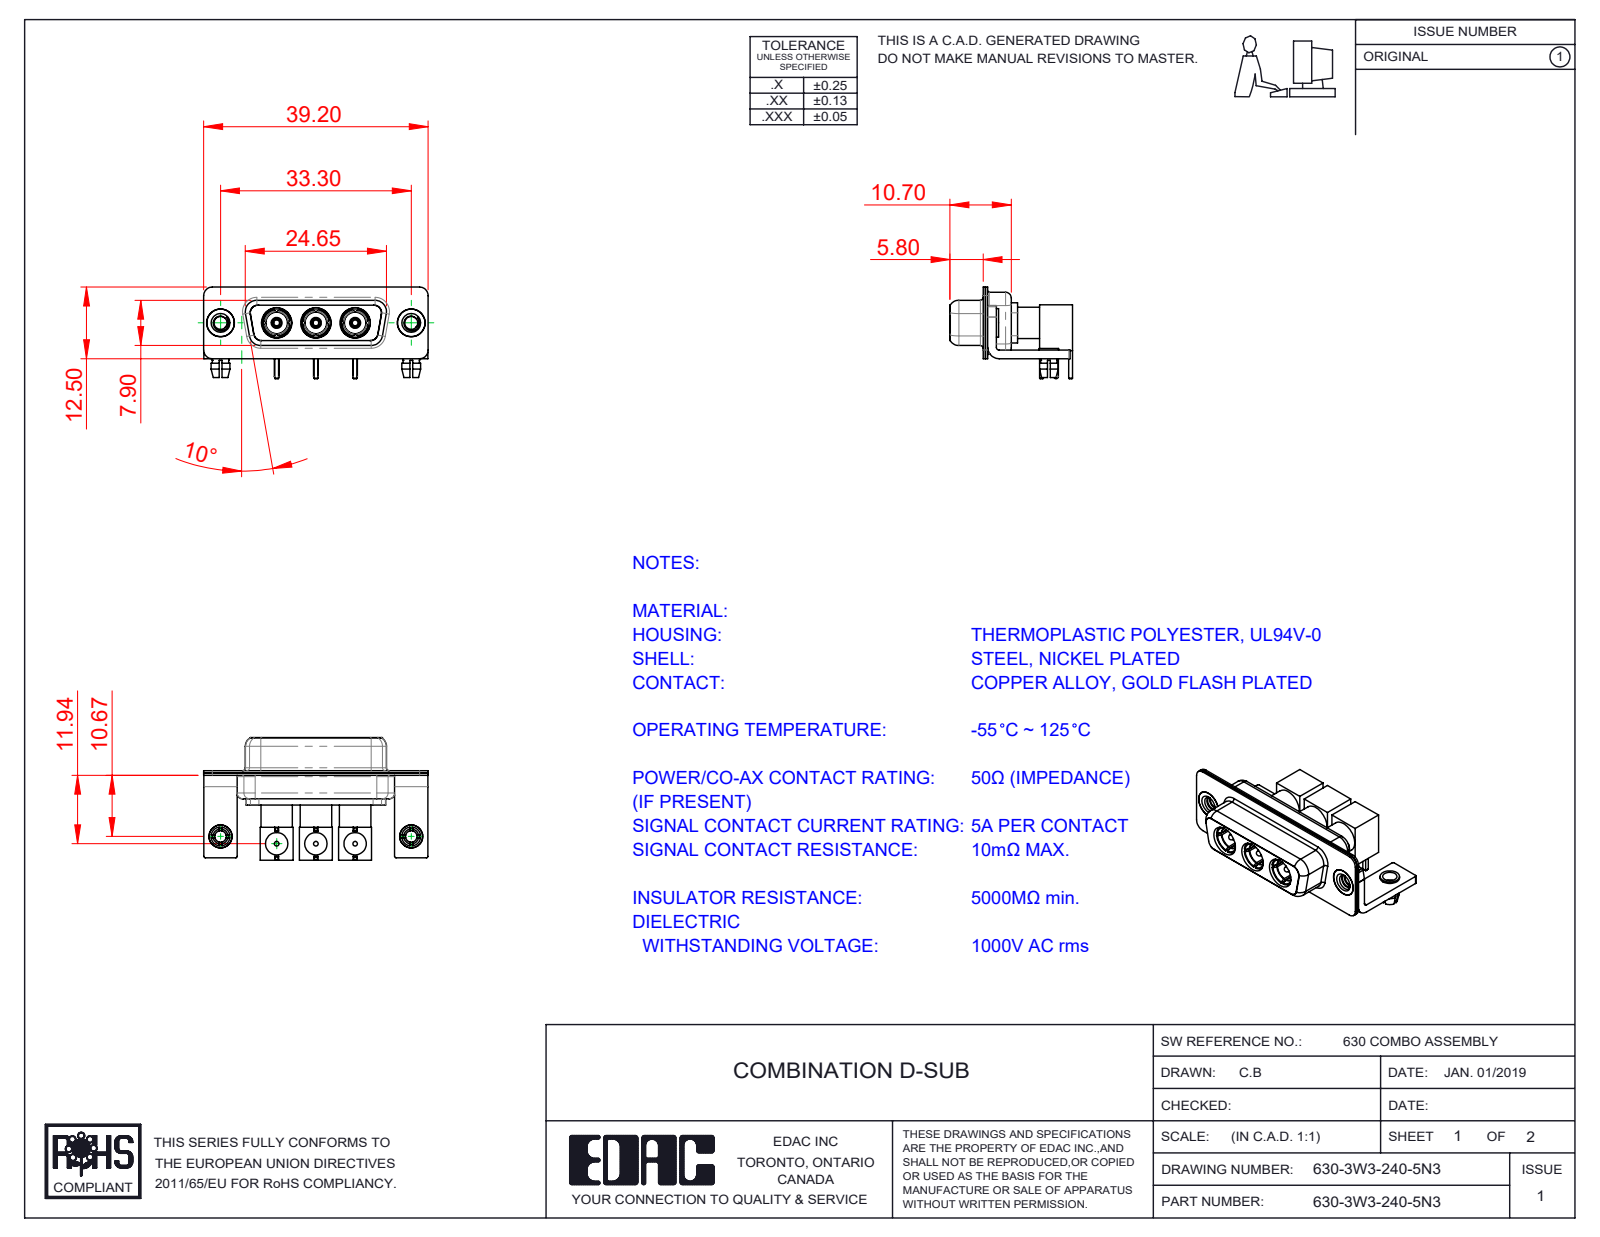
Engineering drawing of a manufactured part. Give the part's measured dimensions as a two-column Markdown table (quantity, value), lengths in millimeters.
| quantity | value |
| --- | --- |
| part name | 630Combo Threaded Rivet_3; Co-Ax Plug_RA PC Tail; 630Combo Stabilizer Bracket; 630-3W3-240-5N3 (+8 more) |
| STEP written by | SolidWorks 2020 (CONFIG_CONTROL_DESIGN) |
| units | millimeters |
| bodies | 27 solids, 915 faces (336 planar, 382 cylindrical, 197 other) |
| overall size | 39.2 × 21.41 × 16 |
| volume | 3 443 mm³ |
| surface area | 8 586 mm² |
| round holes (diameter × count) | 4.85 × 5, 0.8 × 3, 1.1 × 3, 1.5 × 3, 2.83 × 3, 3.1 × 3, 3.3 × 3, 3.9 × 3, 3.92 × 3, 4.1 × 3, 5.3 × 3, 2 × 2 |
| round bosses / shafts (diameter × count) | 5 × 5, 4 × 5, 2.9 × 5, 5.5 × 3, 5.2 × 3, 4.75 × 3, 4.15 × 3, 3.76 × 3 |
| partial cylindrical surfaces (radius × count) | 0.25 × 16, 1.5 × 16, 2 × 13, 1.35 × 12, 1.6 × 8, 0.5 × 5, 0.6 × 4, 0.65 × 4 |
| main face-to-face distances | 0.4, 1.8, 1.4, 0.8, 0.45, 8.45, 8.9, 1.85, 1.5, 5.75 |
| hole center spacings | 6.85, 9.8, 9.88, 13.7, 16.65, 16.7, 23.5, 23.53 |
